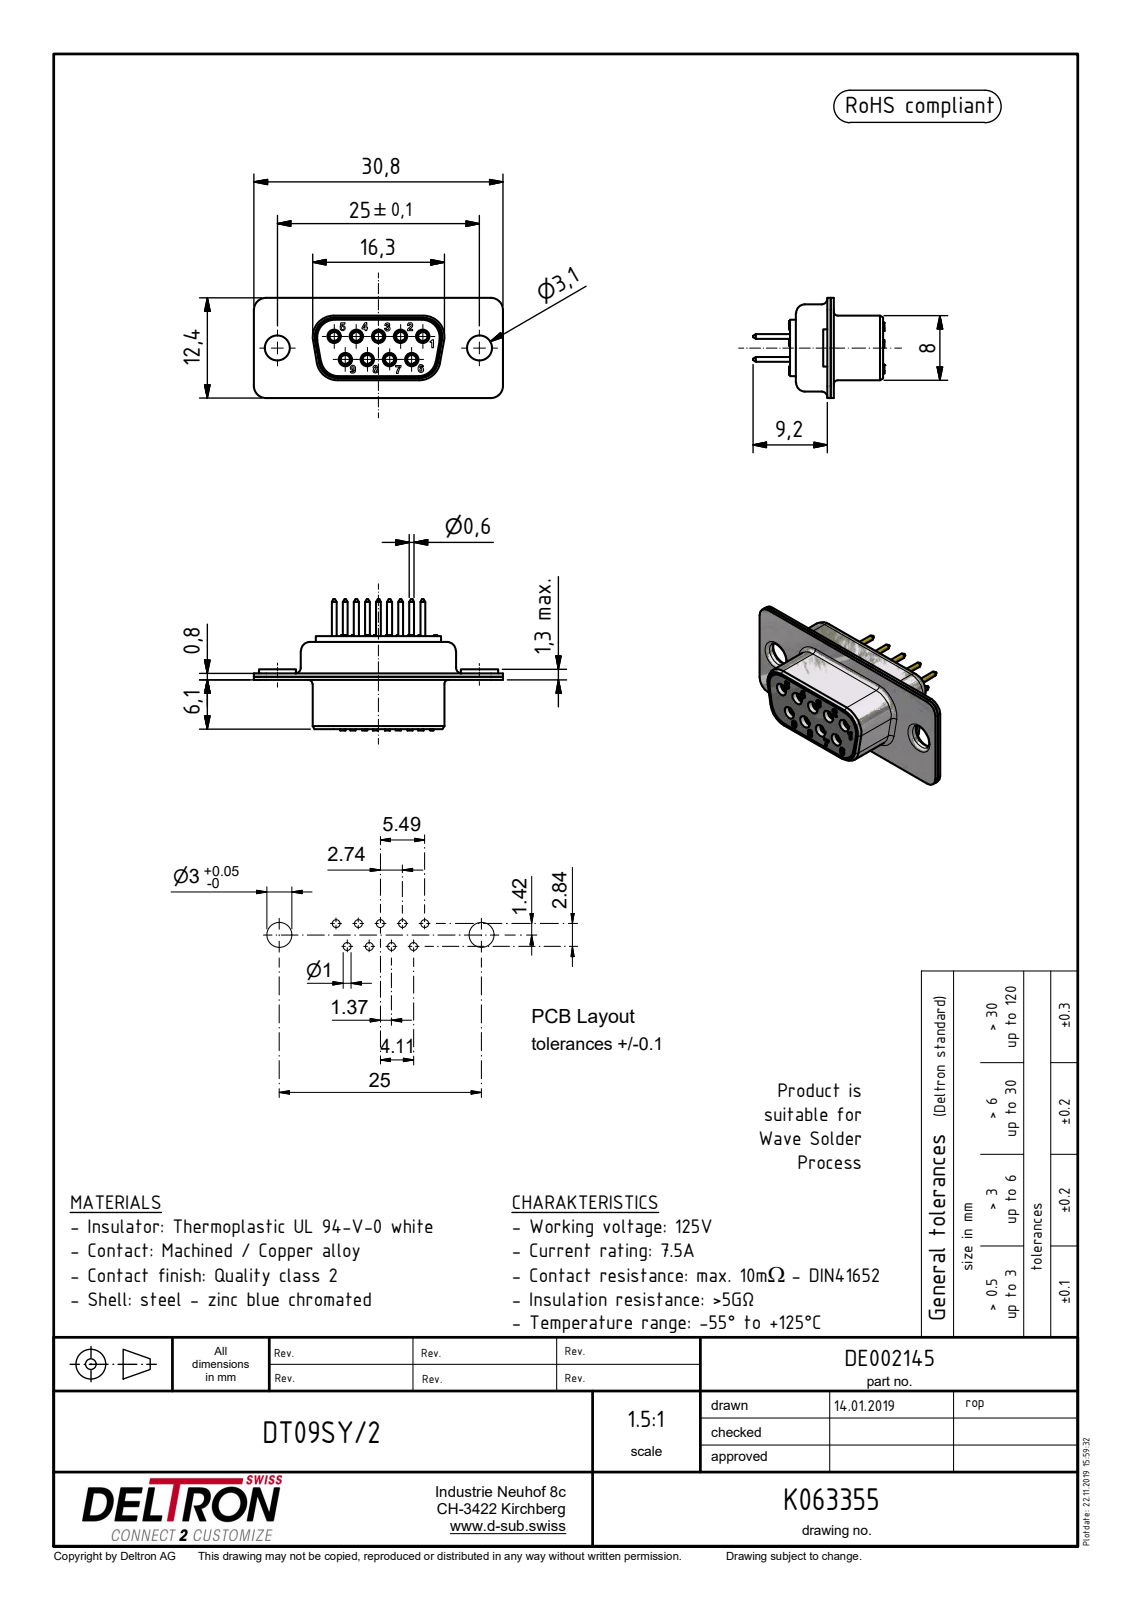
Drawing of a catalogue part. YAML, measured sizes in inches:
part_name: "K063355; N00402_BG; R+B00895_BG; R+B00142_BG (+1 more)"
step_written_by: "Autodesk Inventor 2018 (AUTOMOTIVE_DESIGN)"
units: inches
bodies: {solids: 12, faces: 725, planar: 348, cylindrical: 203, other: 174}
overall_size: [1.213, 0.64, 0.488]
volume: 0.096
surface_area: 6.597
round_holes:
  - {diameter: 0.045, count: 9}
  - {diameter: 0.076, count: 9}
  - {diameter: 0.091, count: 9}
  - {diameter: 0.009, count: 2}
  - {diameter: 0.011, count: 2}
  - {diameter: 0.013, count: 2}
  - {diameter: 0.122, count: 2}
  - {diameter: 0.16, count: 2}
round_bosses_or_shafts:
  - {diameter: 0.088, count: 9}
  - {diameter: 0.077, count: 9}
  - {diameter: 0.067, count: 9}
  - {diameter: 0.063, count: 9}
  - {diameter: 0.024, count: 9}
  - {diameter: 0.181, count: 2}
  - {diameter: 0.154, count: 2}
partial_cylinders:
  - {radius: 0.079, count: 12}
  - {radius: 0.028, count: 8}
  - {radius: 0.043, count: 8}
  - {radius: 0.087, count: 8}
  - {radius: 0.02, count: 4}
  - {radius: 0.035, count: 4}
  - {radius: 0.039, count: 4}
  - {radius: 0.047, count: 4}
face_to_face_distances: [0.016, 0.031, 0.055, 0.02, 0.402, 0.047, 0.051, 0.28, 0.354, 0.386]
hole_center_spacings: [0.124, 0.108, 0.197, 0.216, 0.292, 0.324, 0.078, 0.282]
